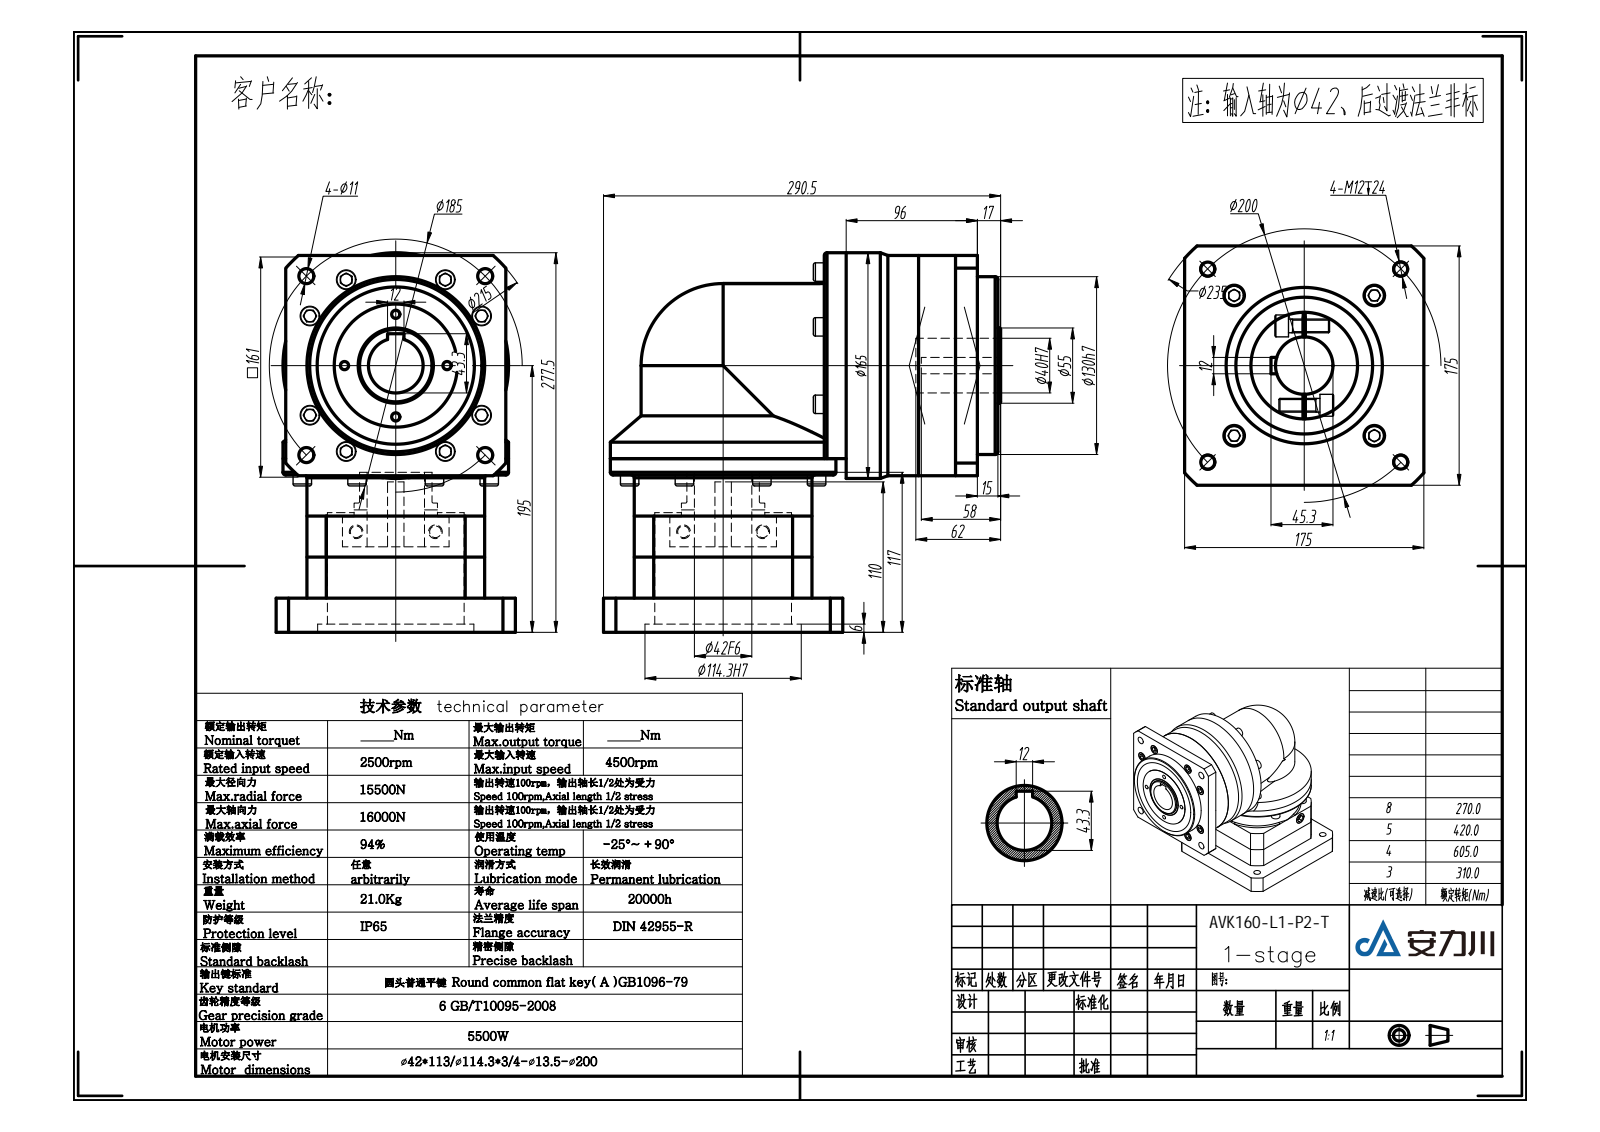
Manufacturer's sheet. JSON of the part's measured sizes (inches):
{"part_name": "VGZE160转角部分-T（42-113 114.3-3 4-13.5-200）; VGK160单级输出部分; VGZK160单级模型-T（42-113 114.3-3 4-13.5-200）", "step_written_by": "SolidWorks 2016 (AUTOMOTIVE_DESIGN)", "units": "inches", "bodies": {"solids": 10, "faces": 552, "planar": 313, "cylindrical": 185, "other": 54}, "overall_size": [11.437, 10.925, 6.89], "volume_in3": 356.9, "surface_area_in2": 793.5, "round_holes": [[0.551, 8], [0.236, 4], [0.268, 4], [0.402, 4], [0.433, 4], [0.591, 4], [0.63, 2], [1.575, 1], [1.654, 1], [2.402, 1], [3.543, 1], [3.937, 1]], "round_bosses_or_shafts": [[0.512, 20], [0.531, 4], [6.496, 2], [5.118, 2], [0.614, 2], [6.339, 1], [4.528, 1], [3.543, 1]], "partial_cylinders_radius": [[2.264, 1], [4.232, 1], [4.528, 1]], "face_to_face_distances": [2.087, 0.984, 4.016, 5, 1.181, 0.886, 2.165, 3.78, 2.835, 6.004], "hole_center_spacings": [2.854, 4.037, 1.153, 1.74, 2.472, 3.813, 4.004, 4.198]}
